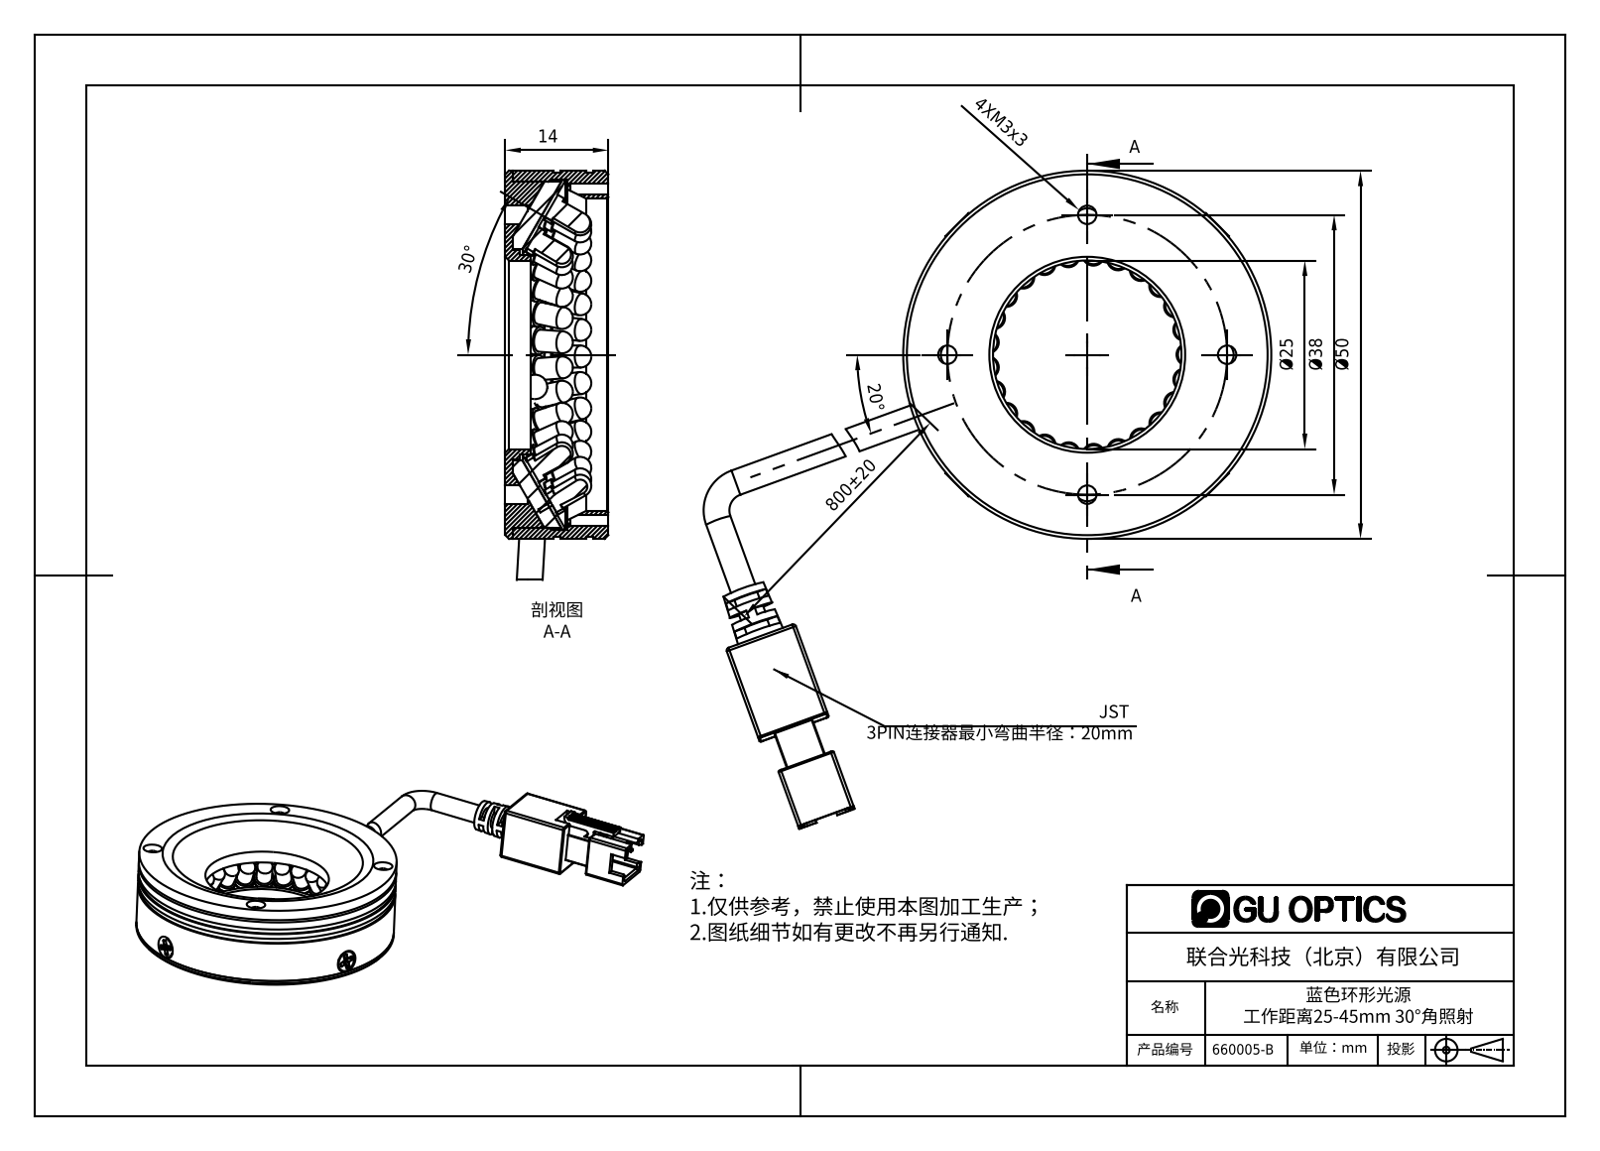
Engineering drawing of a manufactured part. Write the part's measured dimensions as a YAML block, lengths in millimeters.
part_name: "660005-B"
step_written_by: "SolidWorks 2016 (AUTOMOTIVE_DESIGN)"
units: millimeters
bodies: {solids: 67, faces: 1648, planar: 932, cylindrical: 551, other: 165}
overall_size: [93.57, 88.58, 20.28]
volume: 18775
surface_area: 25868
round_holes:
  - {diameter: 1.25, count: 4}
  - {diameter: 1.8, count: 4}
  - {diameter: 2.2, count: 4}
  - {diameter: 2.5, count: 4}
  - {diameter: 2.4, count: 2}
  - {diameter: 24, count: 1}
  - {diameter: 25, count: 1}
  - {diameter: 28.7, count: 1}
  - {diameter: 42.4, count: 1}
  - {diameter: 47.6, count: 1}
round_bosses_or_shafts:
  - {diameter: 3.8, count: 73}
  - {diameter: 3, count: 56}
  - {diameter: 2, count: 4}
  - {diameter: 3.5, count: 2}
  - {diameter: 50, count: 1}
  - {diameter: 49.4, count: 1}
  - {diameter: 47, count: 1}
  - {diameter: 29.2, count: 1}
partial_cylinders:
  - {radius: 0.2, count: 61}
  - {radius: 0.1, count: 15}
  - {radius: 0.4, count: 12}
  - {radius: 0.88, count: 4}
  - {radius: 0.3, count: 1}
  - {radius: 0.68, count: 1}
  - {radius: 1.4, count: 1}
  - {radius: 1.6, count: 1}
face_to_face_distances: [1, 14, 2, 16, 13, 15, 1.2, 12.8, 14.8, 3]
hole_center_spacings: [29.45, 3.5, 19, 22.5, 26.87, 31.82, 41.5, 38]
